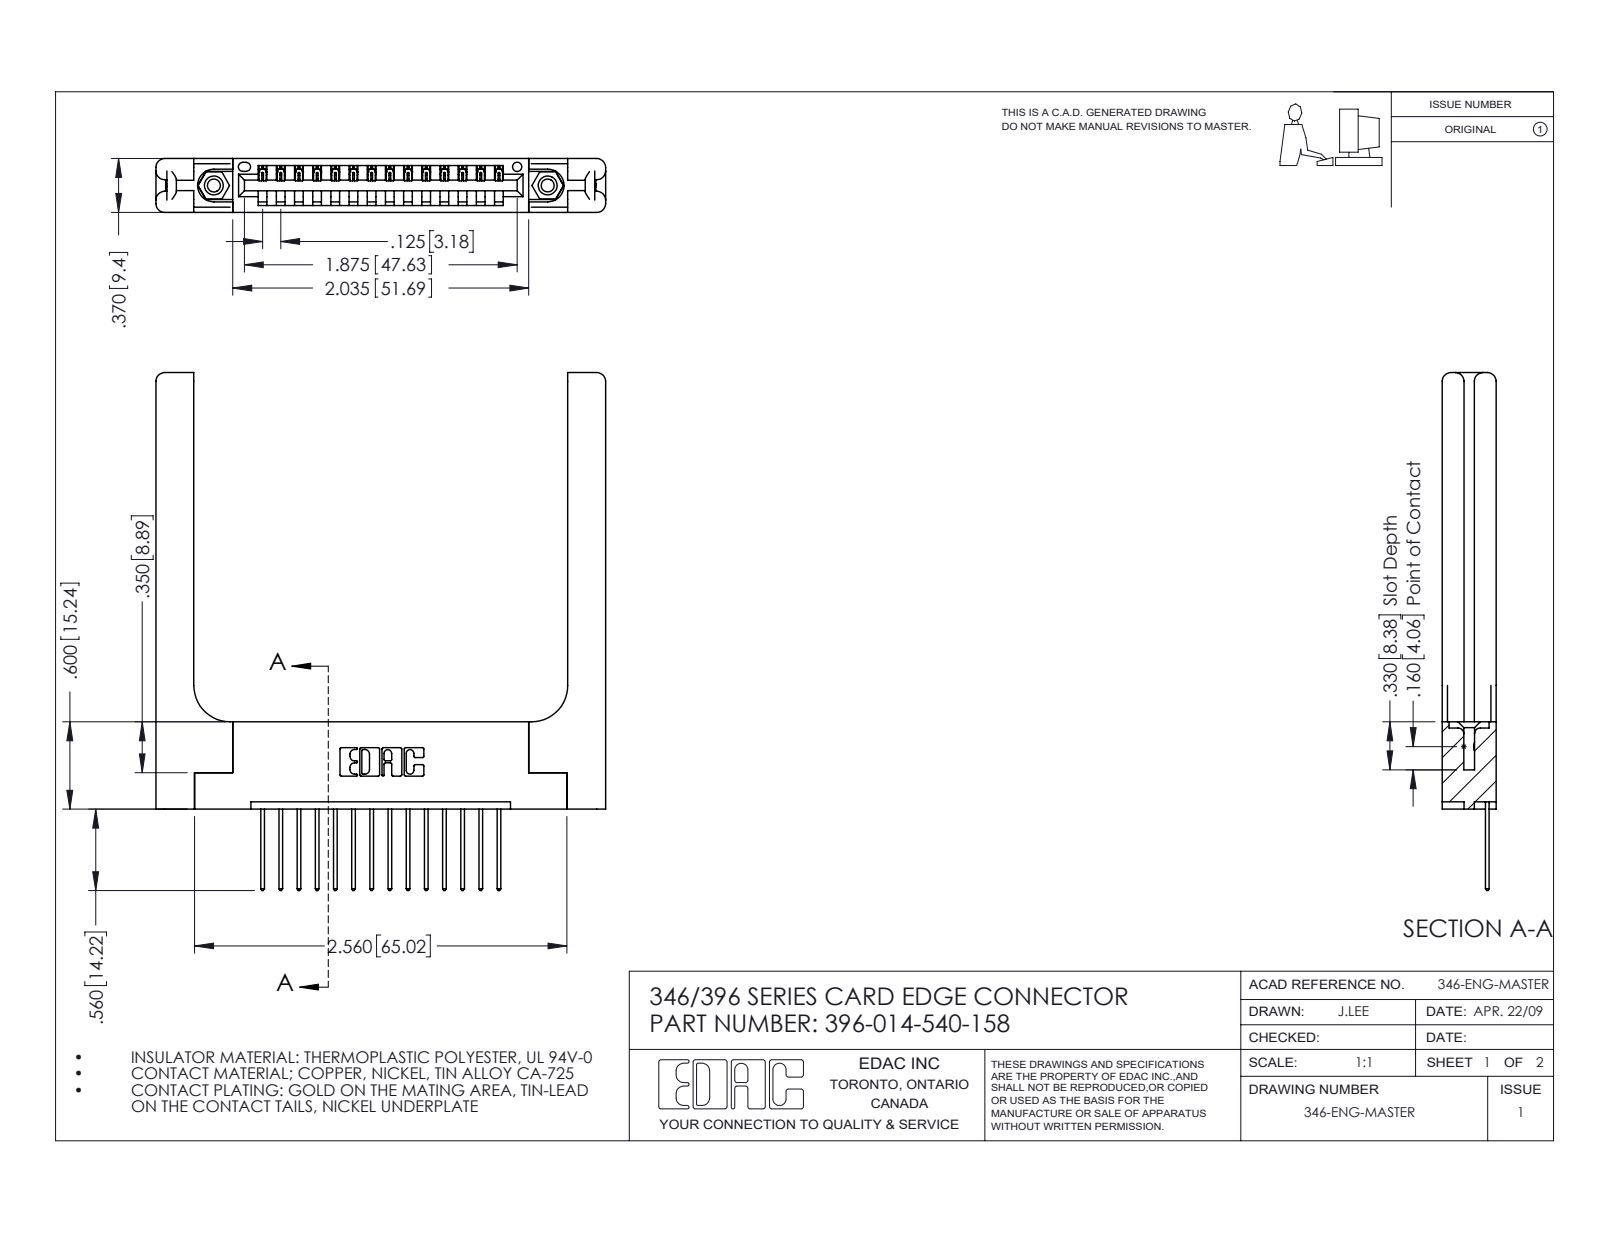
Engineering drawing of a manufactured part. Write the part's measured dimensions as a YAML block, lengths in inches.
part_name: "345-250-001_345-250-001-102; 345-292-001_345-293-140; 396-014-540-158; 346-220-058_345-220-058 (+1 more)"
step_written_by: "SolidWorks 2016 (CONFIG_CONTROL_DESIGN)"
units: inches
bodies: {solids: 19, faces: 1190, planar: 784, cylindrical: 346, other: 60}
overall_size: [3.56, 3.091, 0.37]
volume: 0.907
surface_area: 21.98
round_holes:
  - {diameter: 0.089, count: 2}
  - {diameter: 0.125, count: 2}
  - {diameter: 0.156, count: 2}
  - {diameter: 0.064, count: 1}
round_bosses_or_shafts:
  - {diameter: 0.155, count: 2}
partial_cylinders:
  - {radius: 0.006, count: 28}
  - {radius: 0.01, count: 28}
  - {radius: 0.01, count: 22}
  - {radius: 0.06, count: 16}
  - {radius: 0.007, count: 6}
  - {radius: 0.031, count: 6}
  - {radius: 0.026, count: 3}
  - {radius: 0.03, count: 2}
face_to_face_distances: [0.37, 0.15, 0.072, 0.148, 0.048, 0.322, 0.25, 0.22, 0.102, 0.173]
hole_center_spacings: [0.246, 2.089, 2.295]
